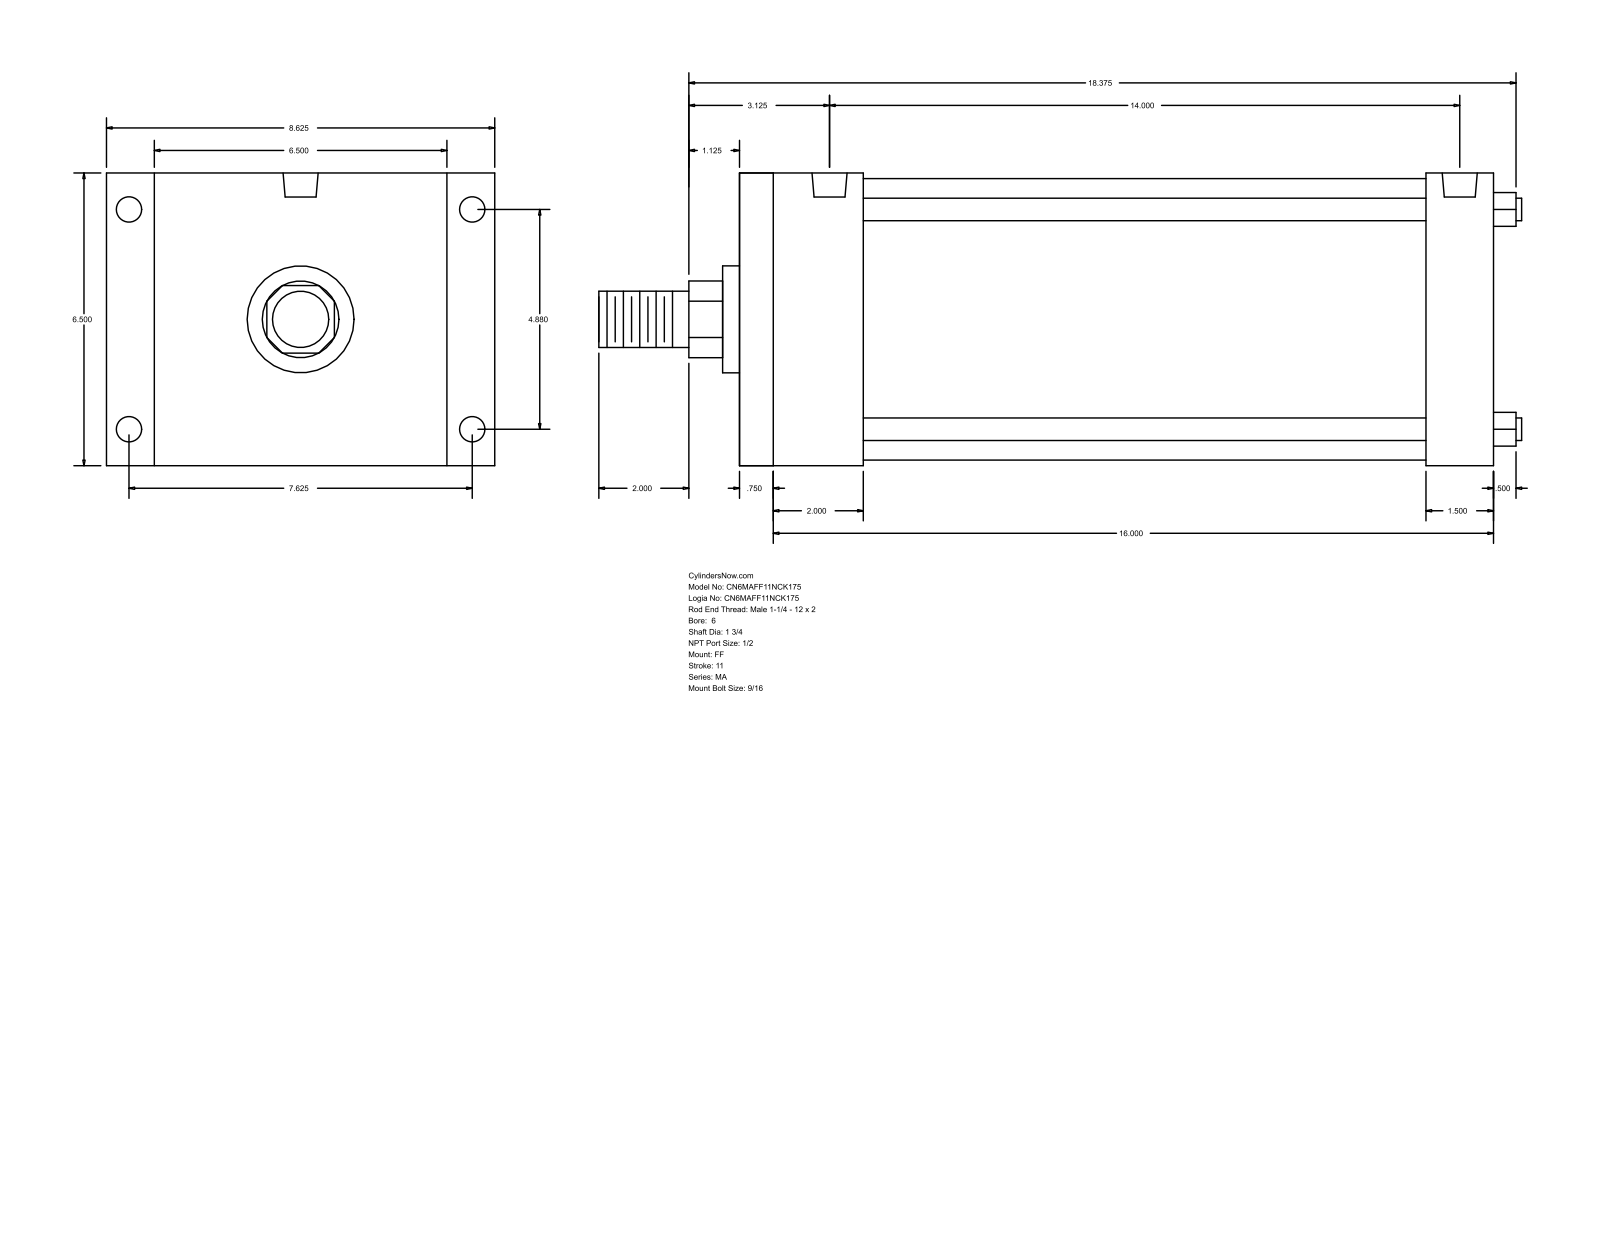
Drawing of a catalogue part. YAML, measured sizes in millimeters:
part_name: "MA_FF__0600_1.75"
step_written_by: "GSSL Pune (CONFIG_CONTROL_DESIGN)"
units: millimeters
bodies: {solids: 0, faces: 92, planar: 64, cylindrical: 28, other: 0}
overall_size: [520.7, 219.07, 165.1]
round_holes:
  - {diameter: 14.29, count: 4}
  - {diameter: 17.46, count: 4}
  - {diameter: 19.77, count: 2}
round_bosses_or_shafts:
  - {diameter: 12.7, count: 4}
  - {diameter: 158.75, count: 1}
  - {diameter: 60.33, count: 1}
  - {diameter: 44.45, count: 1}
  - {diameter: 31.75, count: 1}
partial_cylinders:
  - {radius: 21.63, count: 1}
face_to_face_distances: [165.1, 425.45, 19.05, 406.4, 50.8, 69.85, 368.31, 355.6, 387.36, 317.51]
hole_center_spacings: [123.96, 193.68, 229.95, 355.6]
